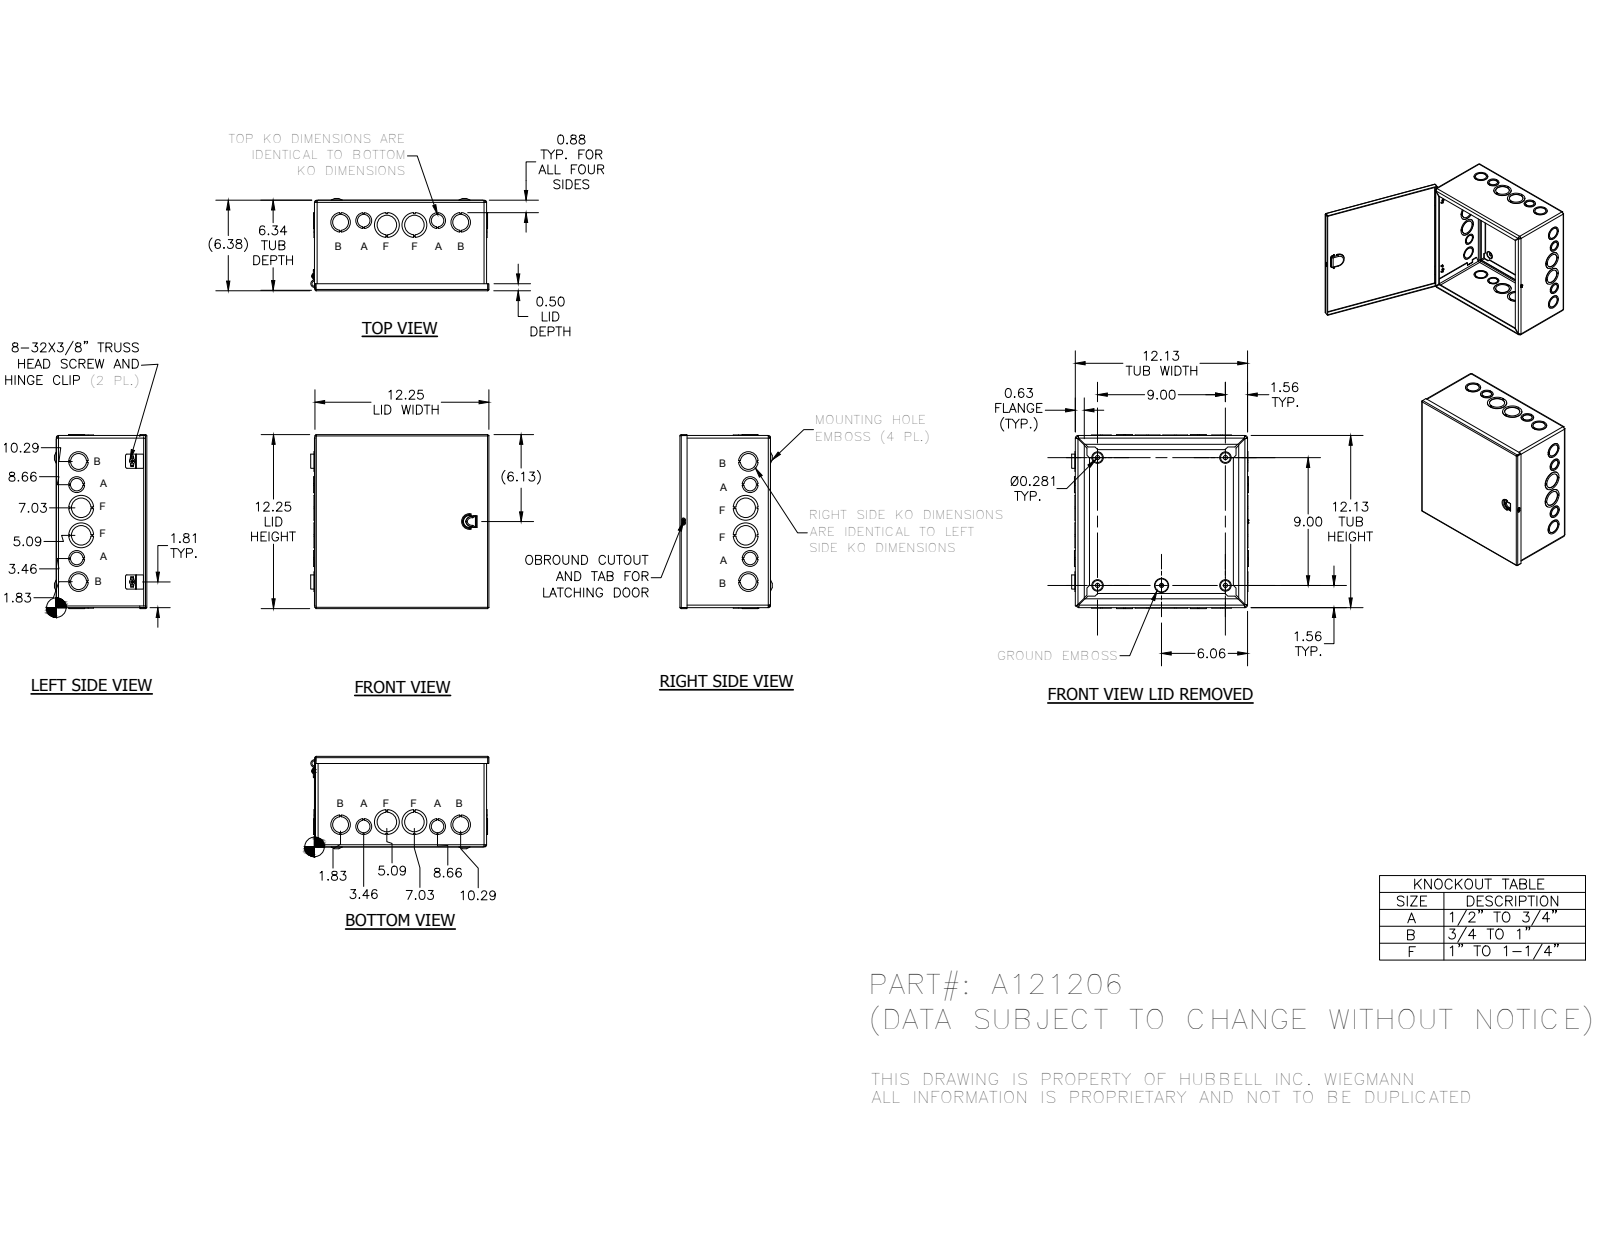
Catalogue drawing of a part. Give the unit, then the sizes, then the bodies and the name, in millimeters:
Units: millimetres
Overall size (bounding box): 320.97 × 315.89 × 165.19
Round holes (diameter × count): ⌀28.57 ×8, ⌀34.92 ×8, ⌀7.62 ×4, ⌀22.22 ×4, ⌀44.45 ×4, ⌀3.56 ×2, ⌀4.19 ×1
Round bosses / shafts (diameter × count): ⌀9.75 ×2, ⌀4.17 ×2, ⌀5.8 ×1
Partial cylindrical surfaces — rounded edges, fillets, slot ends (radius × count): R3.17 ×15, R0.79 ×10, R1.59 ×9, R2.38 ×8, R4.75 ×8, R1.4 ×4, R1.57 ×4, R1.78 ×4
Main face-to-face distances: 1.57, 1.58, 306.4, 160.43, 158.85, 1.59, 304.83, 160.44, 162.02, 307.98
Hole centre spacings: 41.52, 42.15, 82.94, 91.03, 132.17, 173.51, 228.6, 49.28
Bodies: 23 solids, 1167 faces (758 planar, 251 cylindrical, 158 other)
Part name (STEP PRODUCT): A1212BA; A121206WRA; 31816; 372177 (+3 more)
STEP written by: Autodesk Inventor 2014 (AUTOMOTIVE_DESIGN)
